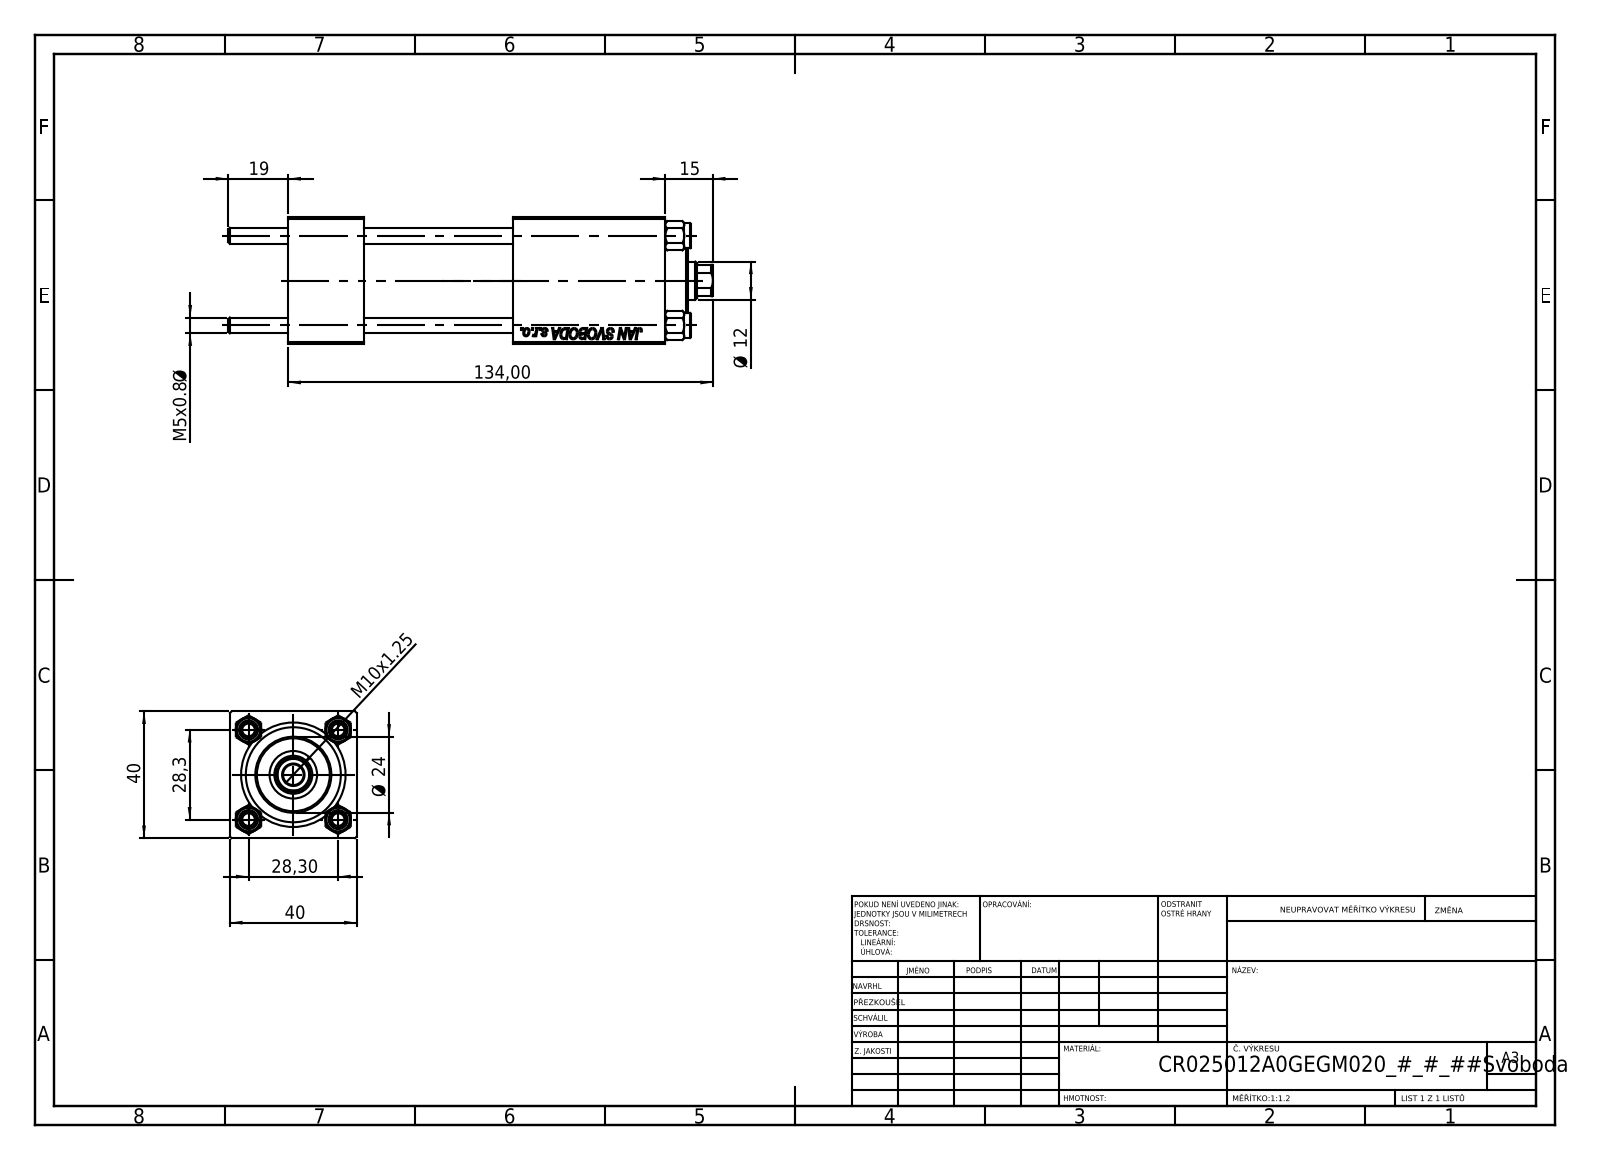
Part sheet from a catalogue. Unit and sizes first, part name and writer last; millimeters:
Units: millimetres
Overall size (bounding box): 153 × 40 × 40
Round holes (diameter × count): ⌀5 ×4, ⌀20 ×3, ⌀7 ×2, ⌀6.5 ×1, ⌀12 ×1, ⌀13 ×1, ⌀13.16 ×1, ⌀15 ×1, ⌀25 ×1, ⌀30 ×1
Round bosses / shafts (diameter × count): ⌀8 ×4, ⌀31 ×1, ⌀24 ×1
Partial cylindrical surfaces — rounded edges, fillets, slot ends (radius × count): R5.5 ×1
Main face-to-face distances: 40, 24, 119, 95, 90.3, 66.3, 28.7, 71, 47, 19.3
Hole centre spacings: 20.01, 28.3, 40.02, 72
Volume: 144 789 mm³ · Surface area: 58 867 mm²
Bodies: 11 solids, 1132 faces (517 planar, 79 cylindrical, 536 other)
Part name (STEP PRODUCT): V215CR_BODY_A; NUT_M5; V215_VC_A; V215CR_VCP (+1 more)
STEP written by: SolidWorks 2019 (CONFIG_CONTROL_DESIGN)
